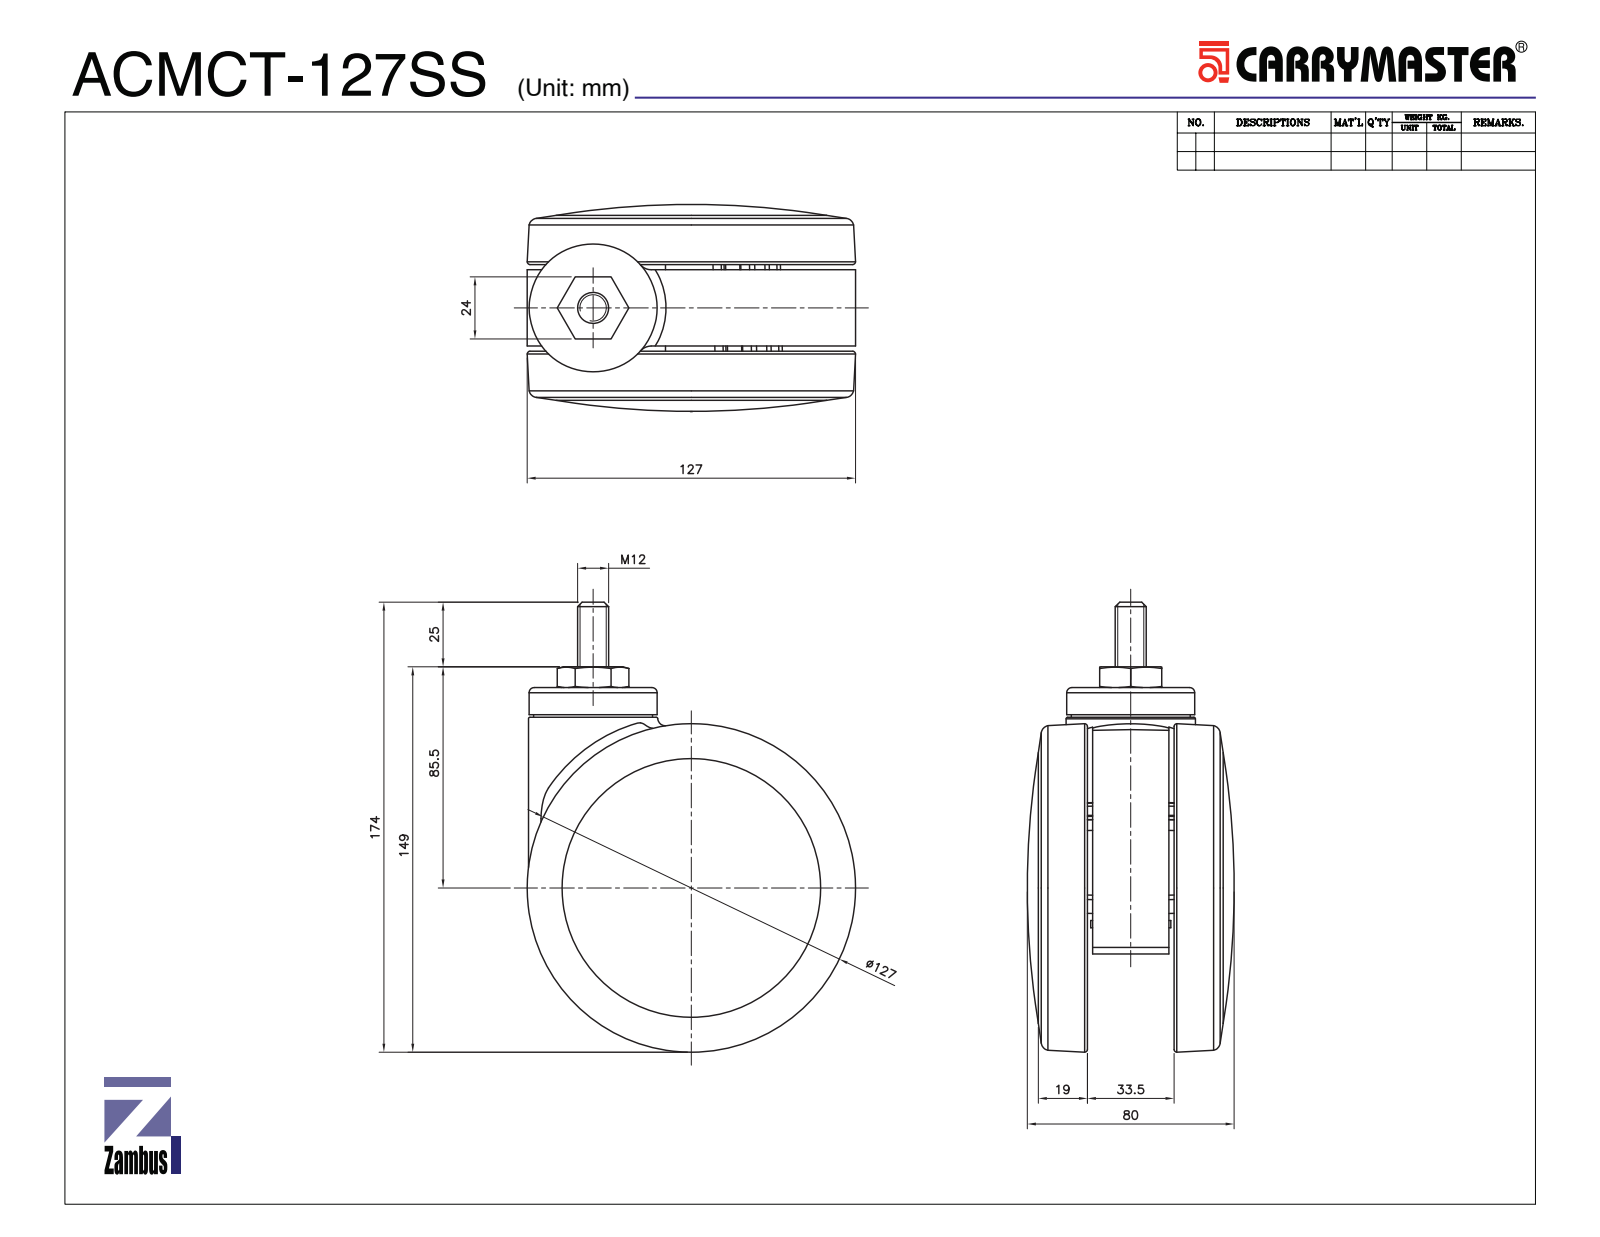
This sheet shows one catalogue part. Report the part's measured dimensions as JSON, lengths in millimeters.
{"part_name": "127 NON BRAKE TYPE FRAME; SS TYPE TOP PLATE; ACMCT-127SS; WHEEL (+1 more)", "step_written_by": "SolidWorks 2019 (CONFIG_CONTROL_DESIGN)", "units": "millimeters", "bodies": {"solids": 5, "faces": 198, "planar": 49, "cylindrical": 94, "other": 55}, "overall_size": [174, 127, 79.99], "volume_mm3": 711016, "surface_area_mm2": 111539, "round_holes": [[30, 1], [93, 1], [100.2, 1]], "round_bosses_or_shafts": [[46, 2], [100, 1], [50, 1], [45, 1], [17, 1], [10.25, 1], [5, 1]], "partial_cylinders_radius": [[0.5, 4], [60.5, 1], [63.5, 1], [66, 1]], "face_to_face_distances": [43.5, 12, 41.5, 10, 2, 31.5, 29.5, 53.5, 33.5, 5]}
